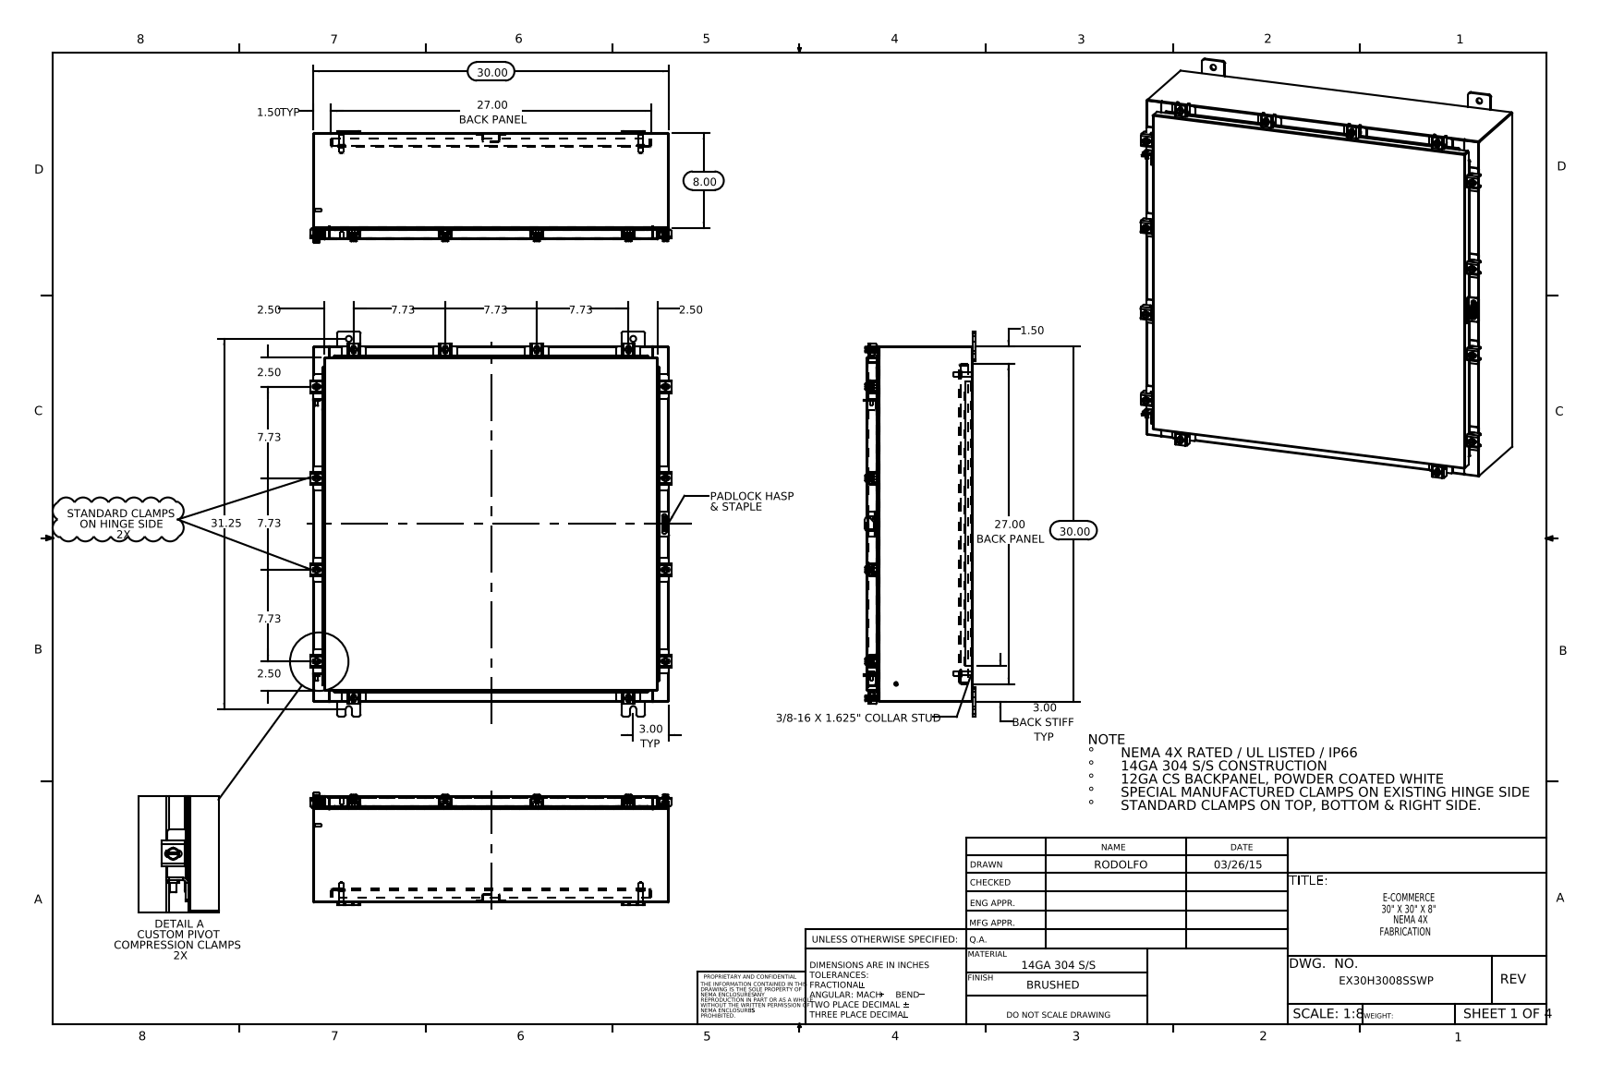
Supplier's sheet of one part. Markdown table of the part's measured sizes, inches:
| quantity | value |
| --- | --- |
| part name | EX30H3008SSWP Clamp Assembly; EX30H3008SSWP Clamp Bracket; EX30H3008SSWP Bottom; EX30H3008SSWP Body (+8 more) |
| STEP written by | SolidWorks 2014 (CONFIG_CONTROL_DESIGN) |
| units | inches |
| bodies | 92 solids, 2310 faces (1241 planar, 893 cylindrical, 176 other) |
| overall size | 32.5 × 30.421 × 9.453 |
| volume | 324.9 in³ |
| surface area | 8 062 in² |
| round holes (diameter × count) | 0.213 × 14, 0.26 × 14, 0.5 × 8, 0.125 × 1, 0.25 × 1 |
| round bosses / shafts (diameter × count) | 0.5 × 14, 0.25 × 14, 0.399 × 12, 0.625 × 4, 0.375 × 4, 0.33 × 4, 0.315 × 2, 0.236 × 2 |
| partial cylindrical surfaces (radius × count) | 0.06 × 62, 0.013 × 30, 0.141 × 28, 0.088 × 26, 0.12 × 26, 0.19 × 24, 0.09 × 22, 0.05 × 21 |
| main face-to-face distances | 0.075, 8.9, 29.925, 8.826, 8.975, 0.104, 1, 1.075, 7.826, 7.9 |
| hole center spacings | 26.506, 36.532, 2.34, 24.31, 27.37, 29.451, 30.449, 4.429 |
